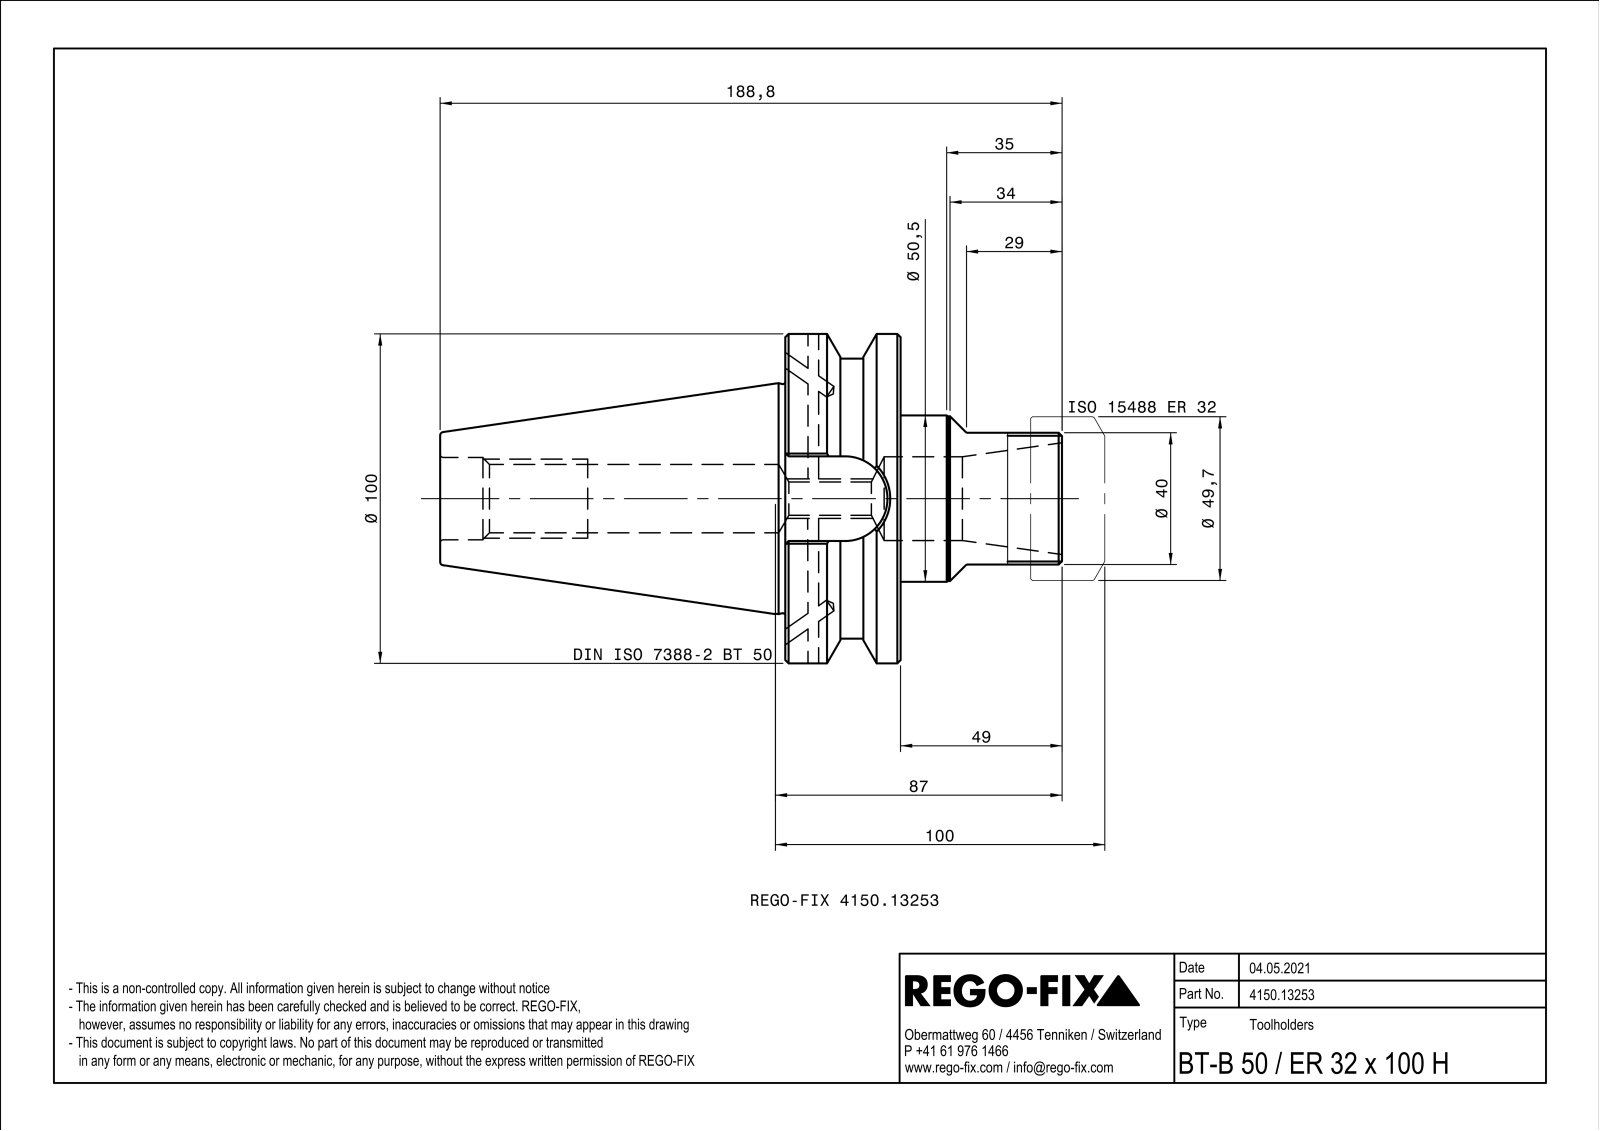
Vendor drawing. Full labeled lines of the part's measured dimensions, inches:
Part name (STEP PRODUCT): NOCUT
STEP written by: SIEMENS PLM Software Solid Edge ST10 (AUTOMOTIVE_DESIGN)
Units: inches
Bodies: 1 solid, 101 faces (28 planar, 31 cylindrical, 42 other)
Overall size (bounding box): 7.433 × 3.937 × 3.937
Volume: 30.34 in³ · Surface area: 98.79 in²
Round holes (diameter × count): ⌀0.128 ×2, ⌀0.154 ×2, ⌀0.398 ×1, ⌀0.817 ×1, ⌀0.925 ×1, ⌀0.984 ×1
Round bosses / shafts (diameter × count): ⌀3.937 ×1, ⌀3.346 ×1, ⌀1.988 ×1, ⌀1.969 ×1, ⌀1.575 ×1
Partial cylindrical surfaces — rounded edges, fillets, slot ends (radius × count): R0.02 ×4, R0.506 ×1
Main face-to-face distances: 1.378, 2.783, 5.504, 4.126, 1.012, 1.929, 3.307, 7.433, 2.374, 0.445
